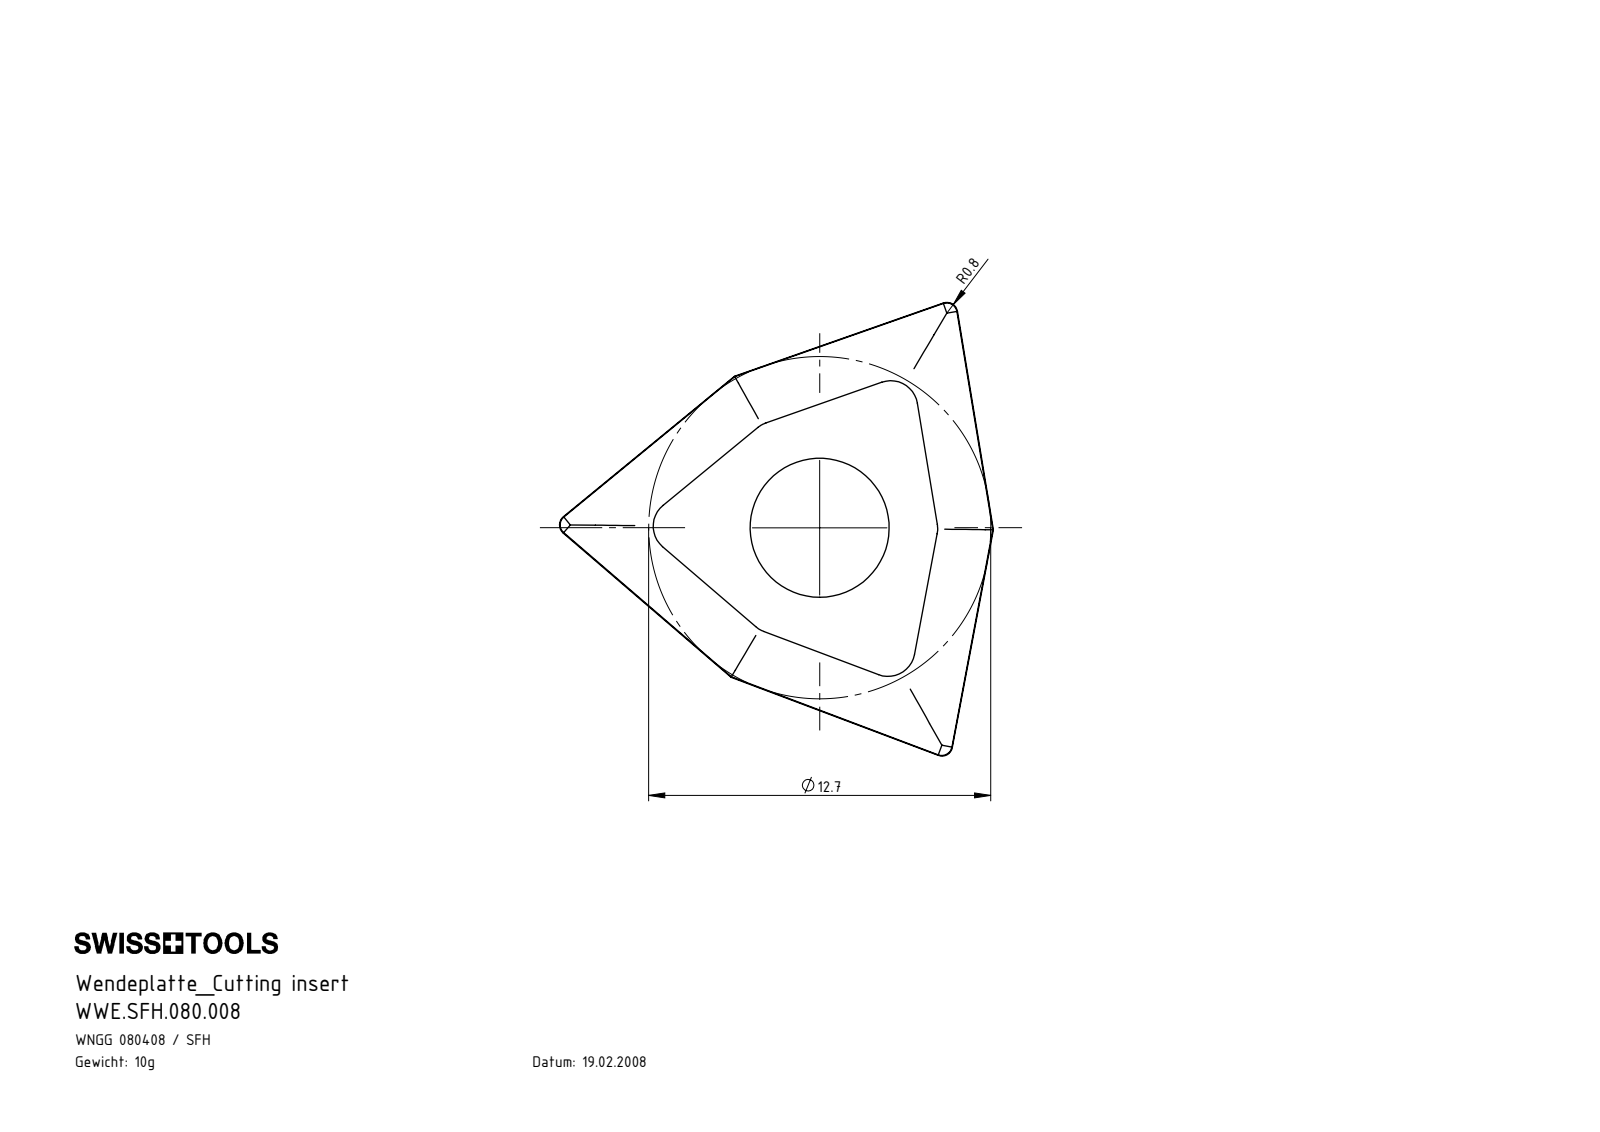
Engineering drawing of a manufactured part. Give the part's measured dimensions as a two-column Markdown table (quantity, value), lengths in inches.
| quantity | value |
| --- | --- |
| part name | WWE.SFH.080.008 |
| STEP written by | SolidWorks 2022 (AUTOMOTIVE_DESIGN) |
| units | inches |
| bodies | 1 solid, 55 faces (21 planar, 6 cylindrical, 28 other) |
| overall size | 0.663 × 0.634 × 0.187 |
| volume | 0.041 in³ |
| surface area | 0.958 in² |
| round holes (diameter × count) | 0.203 × 1 |
| partial cylindrical surfaces (radius × count) | 0.016 × 3 |
| main face-to-face distances | 0.187 |
